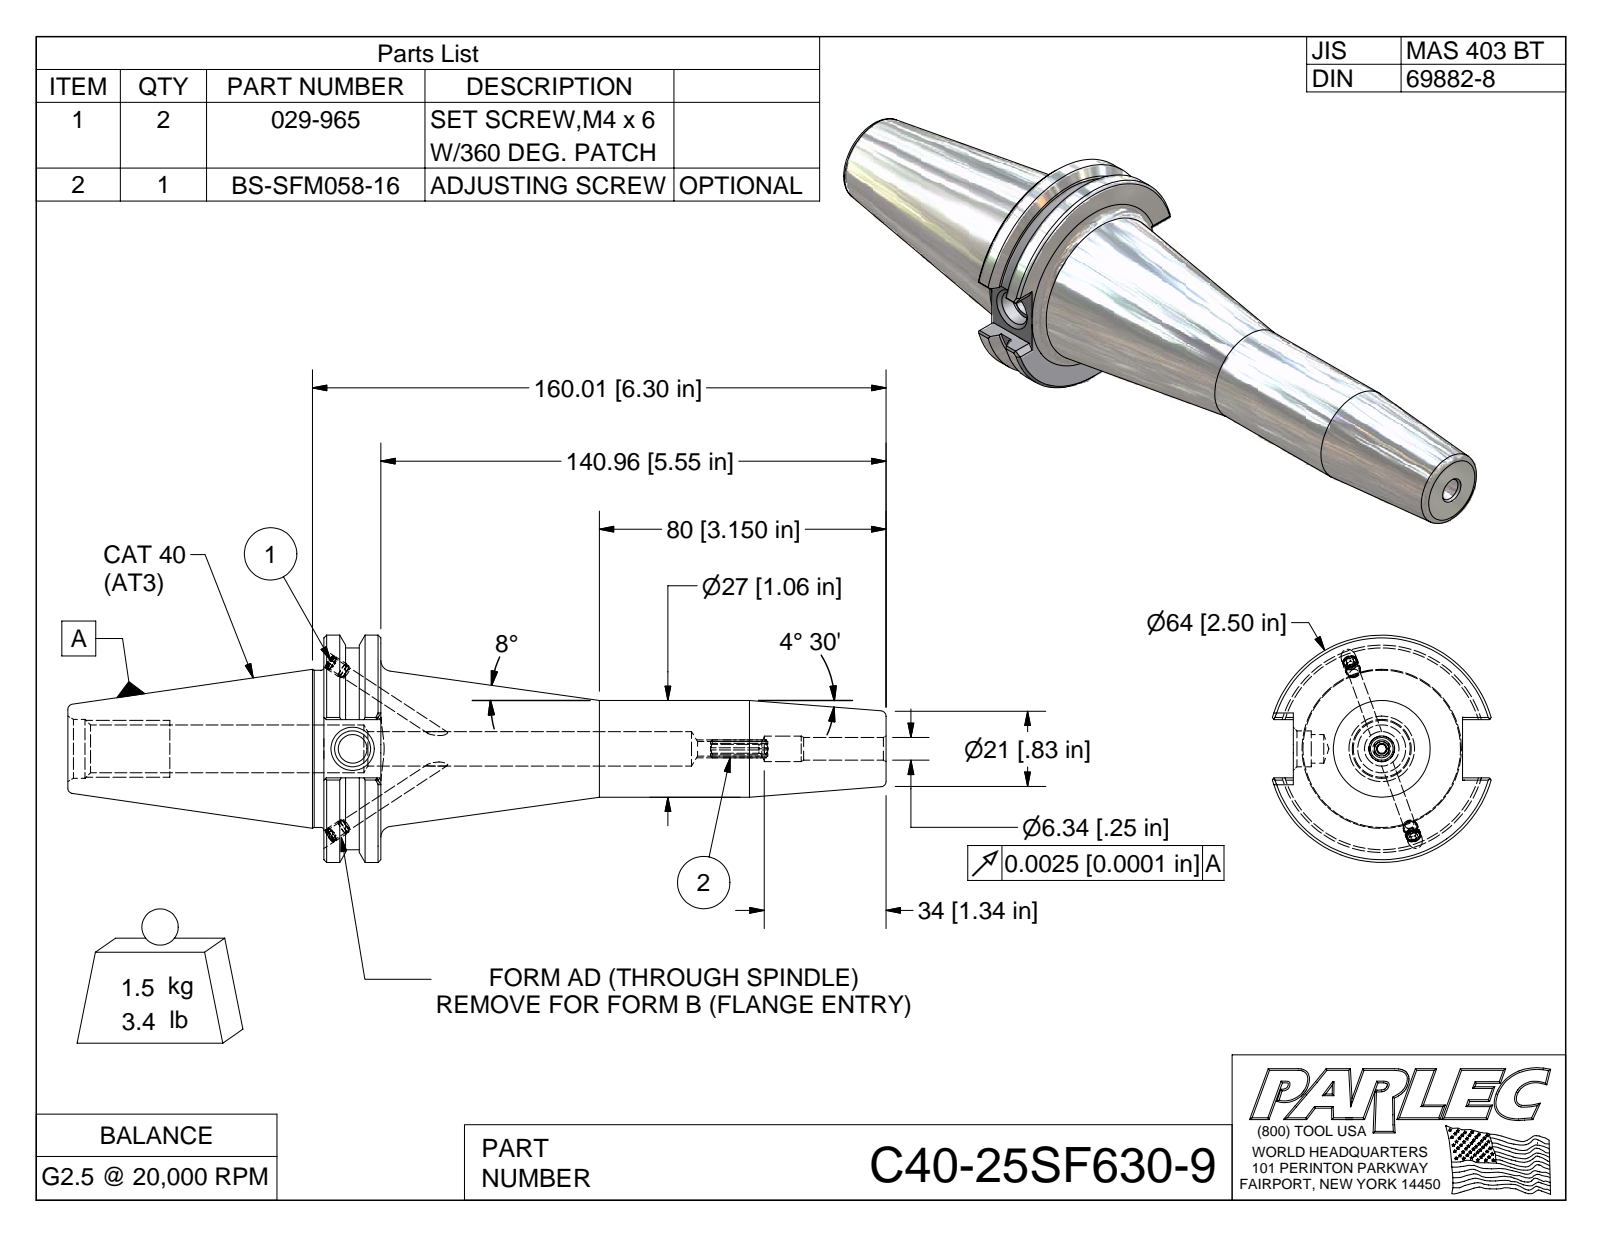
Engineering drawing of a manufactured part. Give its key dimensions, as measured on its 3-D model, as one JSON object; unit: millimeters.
{"part_name": "C40-25SF630-9; C40BC-25SF630-9-1; 029-965; BS-SFM058-16", "step_written_by": "Autodesk Inventor 2009 (AUTOMOTIVE_DESIGN)", "units": "millimeters", "bodies": {"solids": 4, "faces": 134, "planar": 66, "cylindrical": 22, "other": 46}, "overall_size": [228.3, 63.5, 61], "volume_mm3": 195700, "surface_area_mm2": 37300, "round_holes": [[3.3, 2], [4.1, 2], [6.4, 1], [7.1, 1]], "round_bosses_or_shafts": [[4.2, 2], [4, 2], [63.5, 1], [56.4, 1], [43.9, 1], [27, 1]], "partial_cylinders_radius": [[2.5, 1]], "face_to_face_distances": [15.9, 156.8, 141, 16.3, 47.2, 71.4, 87.3, 228.3, 81.3, 9.9]}
